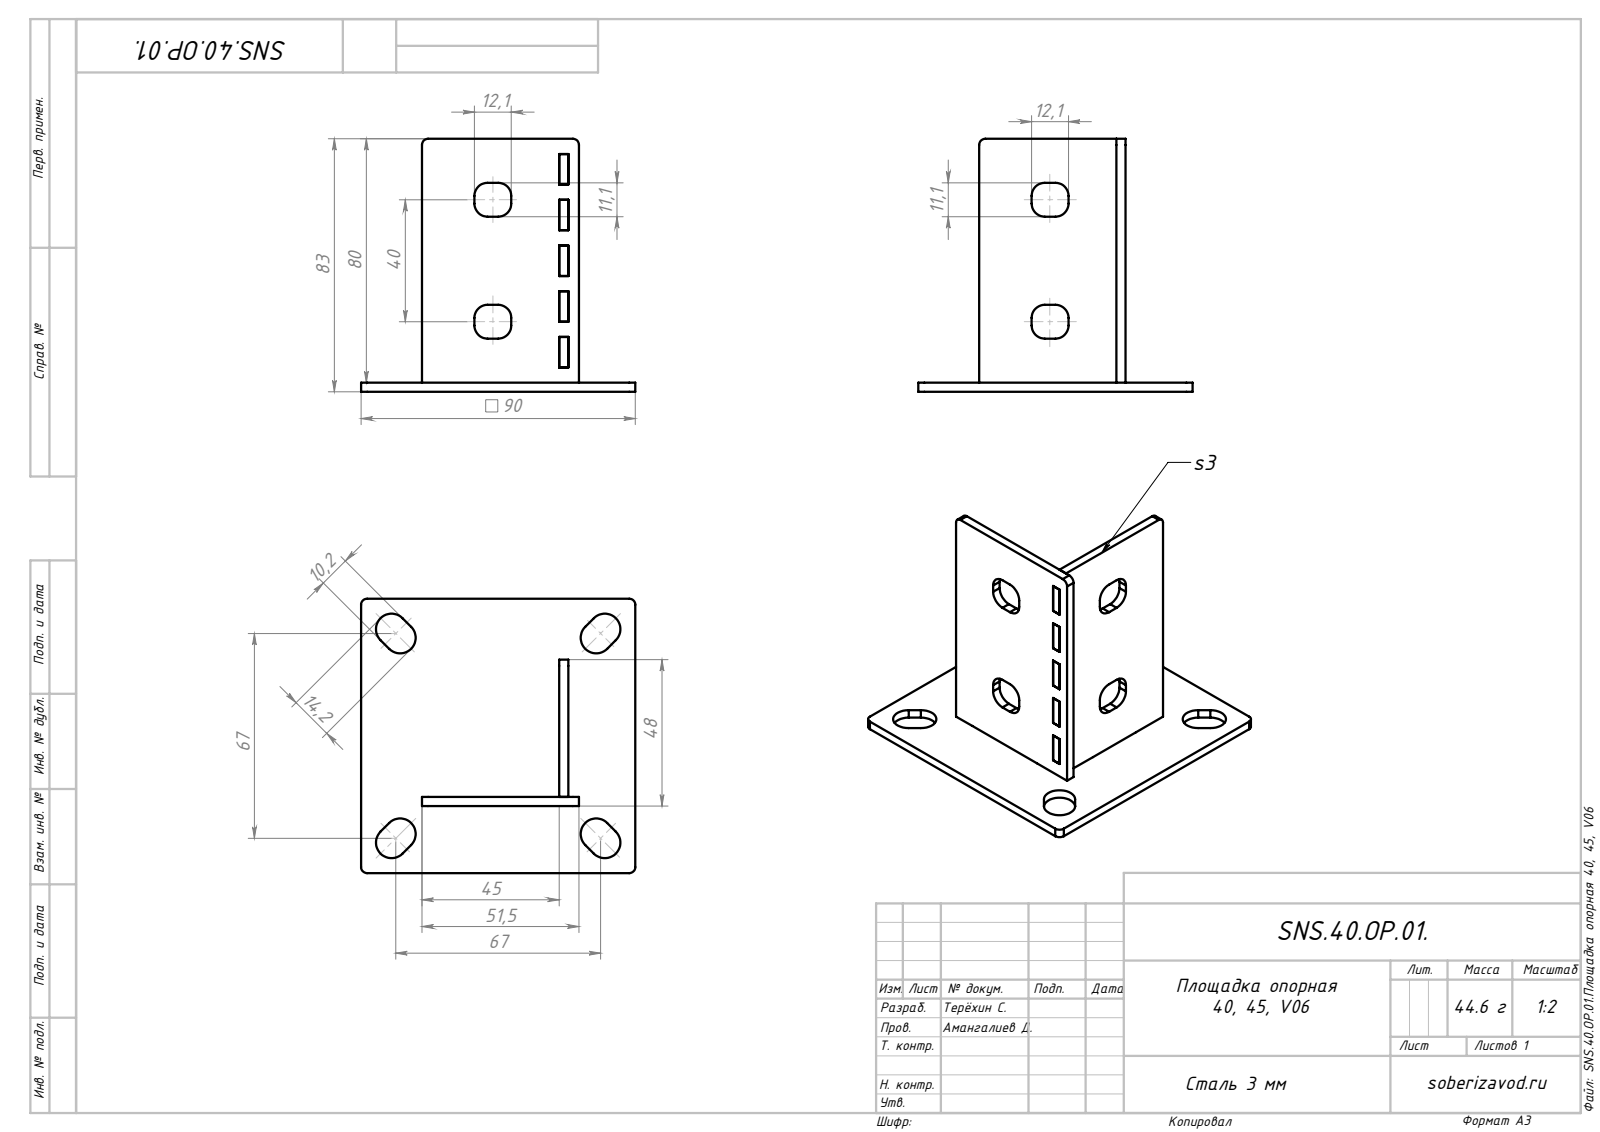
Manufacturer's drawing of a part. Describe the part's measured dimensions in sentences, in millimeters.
The part is named "Боковина с пазом 2; 40пластина низ_40; Боковина с пазом 1; 40пластина низ". Its 3-D file was written by "SolidWorks 2017 (AUTOMOTIVE_DESIGN)". It is 3 solids with 133 faces: 98 planar, 35 cylindrical and 0 other. Overall it measures 90 by 90 by 83 millimeters. Its volume is 44 551 cubic millimeters and its surface area 34 102 square millimeters. Partial cylindrical surfaces (rounded edges, fillets, slot ends): 16 of radius 4.3, 8 of radius 5.1, 7 of radius 2. The main face-to-face distances are 3, 25, 20, 45, 65, 68, 90, 22, 48, 70.
